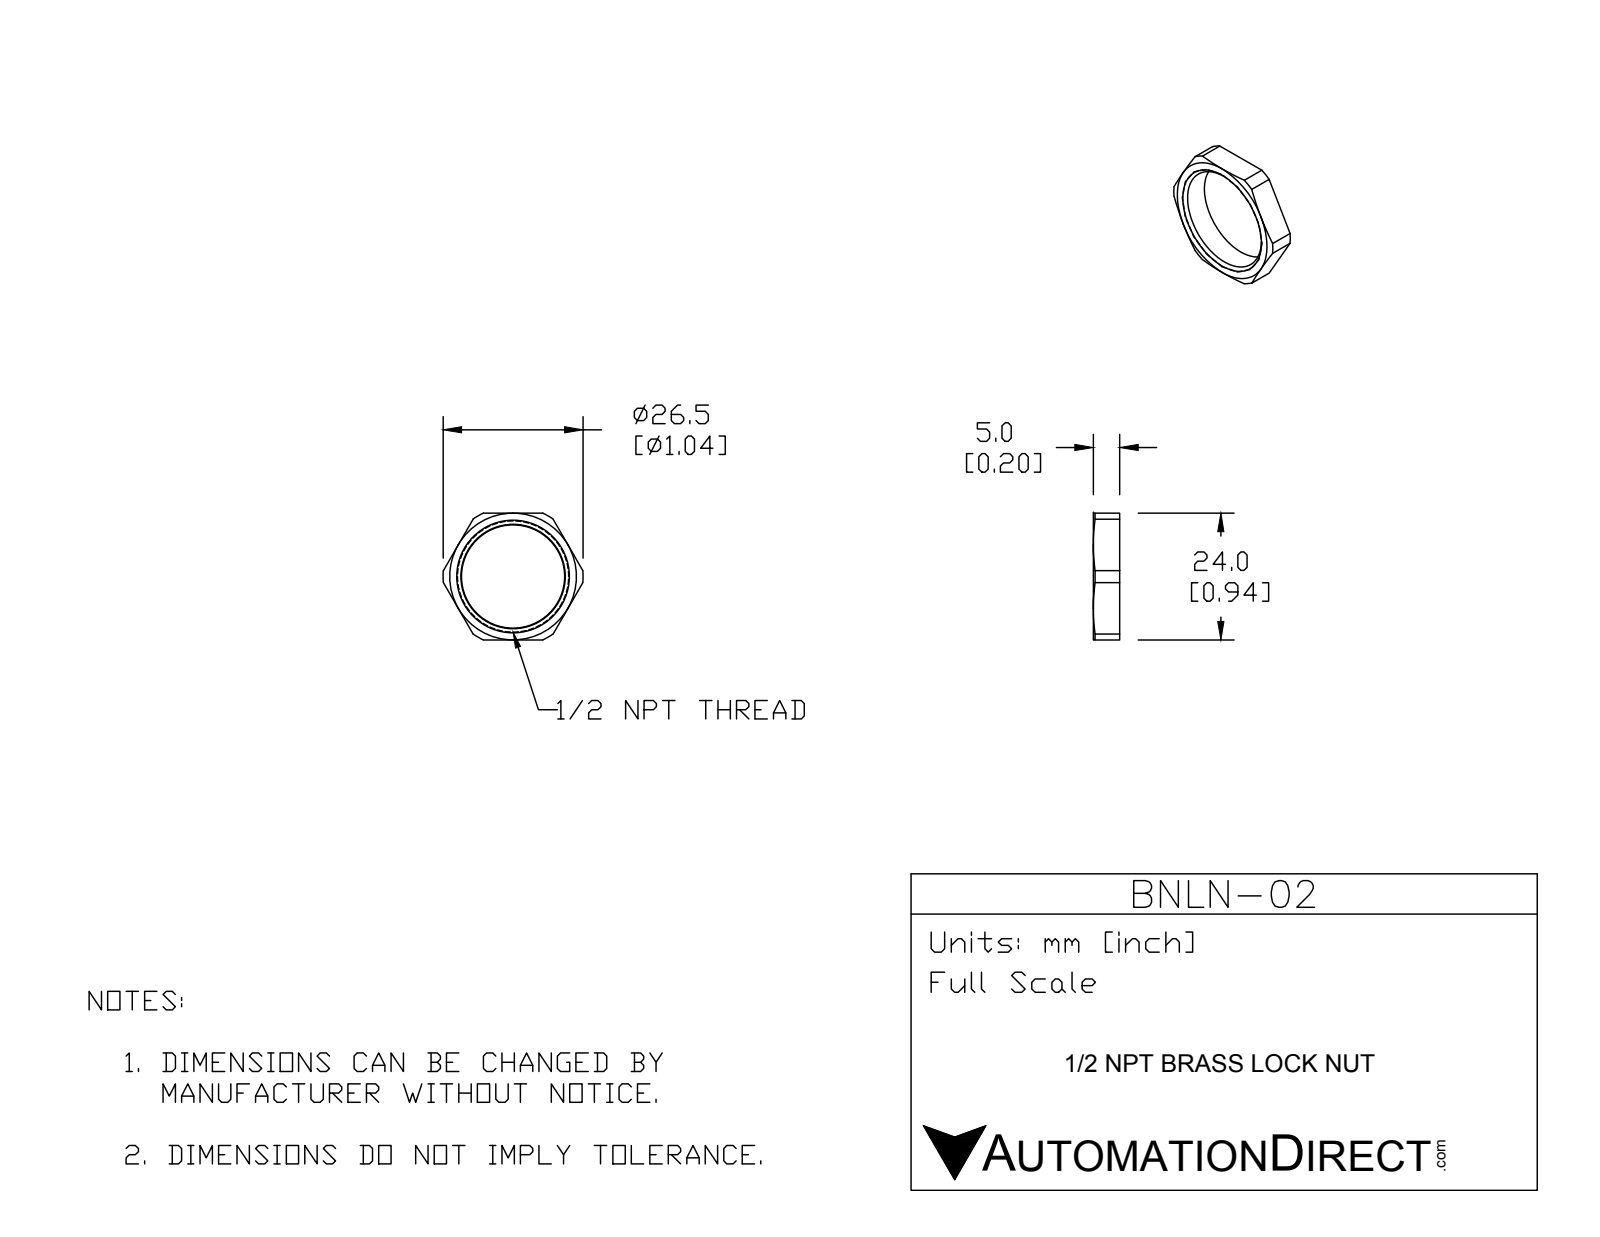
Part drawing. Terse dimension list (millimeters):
name: BNLN-02
written by: SolidWorks 2015 (CONFIG_CONTROL_DESIGN)
unit: mm
bodies: 1 solid, 25 faces (8 planar, 7 cylindrical, 10 other)
size: 26.5 × 24 × 5
volume: 938 mm³; area: 1 064 mm²
rounds: 1× R13.25
face distances: 24, 5
